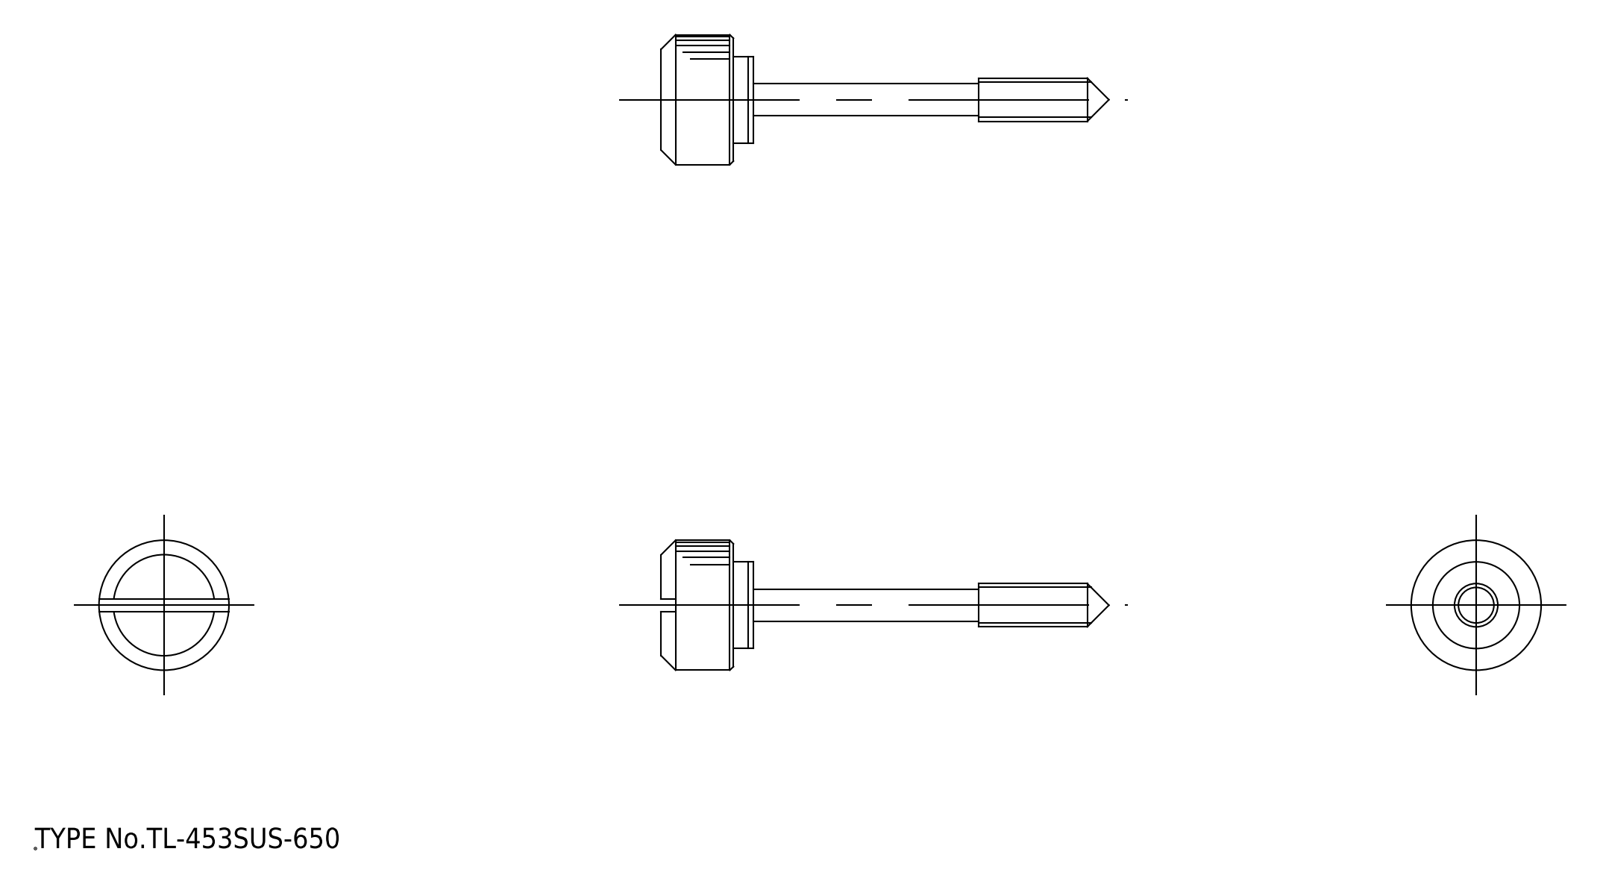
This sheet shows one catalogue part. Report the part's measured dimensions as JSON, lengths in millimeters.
{"part_name": "washer; knob", "step_written_by": "spGate 19.8.4 (****-****-****-****) (AUTOMOTIVE_DESIGN)", "units": "millimeters", "bodies": {"solids": 2, "faces": 42, "planar": 18, "cylindrical": 18, "other": 6}, "overall_size": [62, 18, 18], "volume_mm3": 3633, "surface_area_mm2": 2113, "round_bosses_or_shafts": [[18, 1], [12, 1], [6, 1], [4.5, 1]], "partial_cylinders_radius": [[1, 4], [2.3, 1]], "face_to_face_distances": [2, 10, 12, 12.8, 2.8, 0.8, 8, 10.8, 1.8, 44]}
